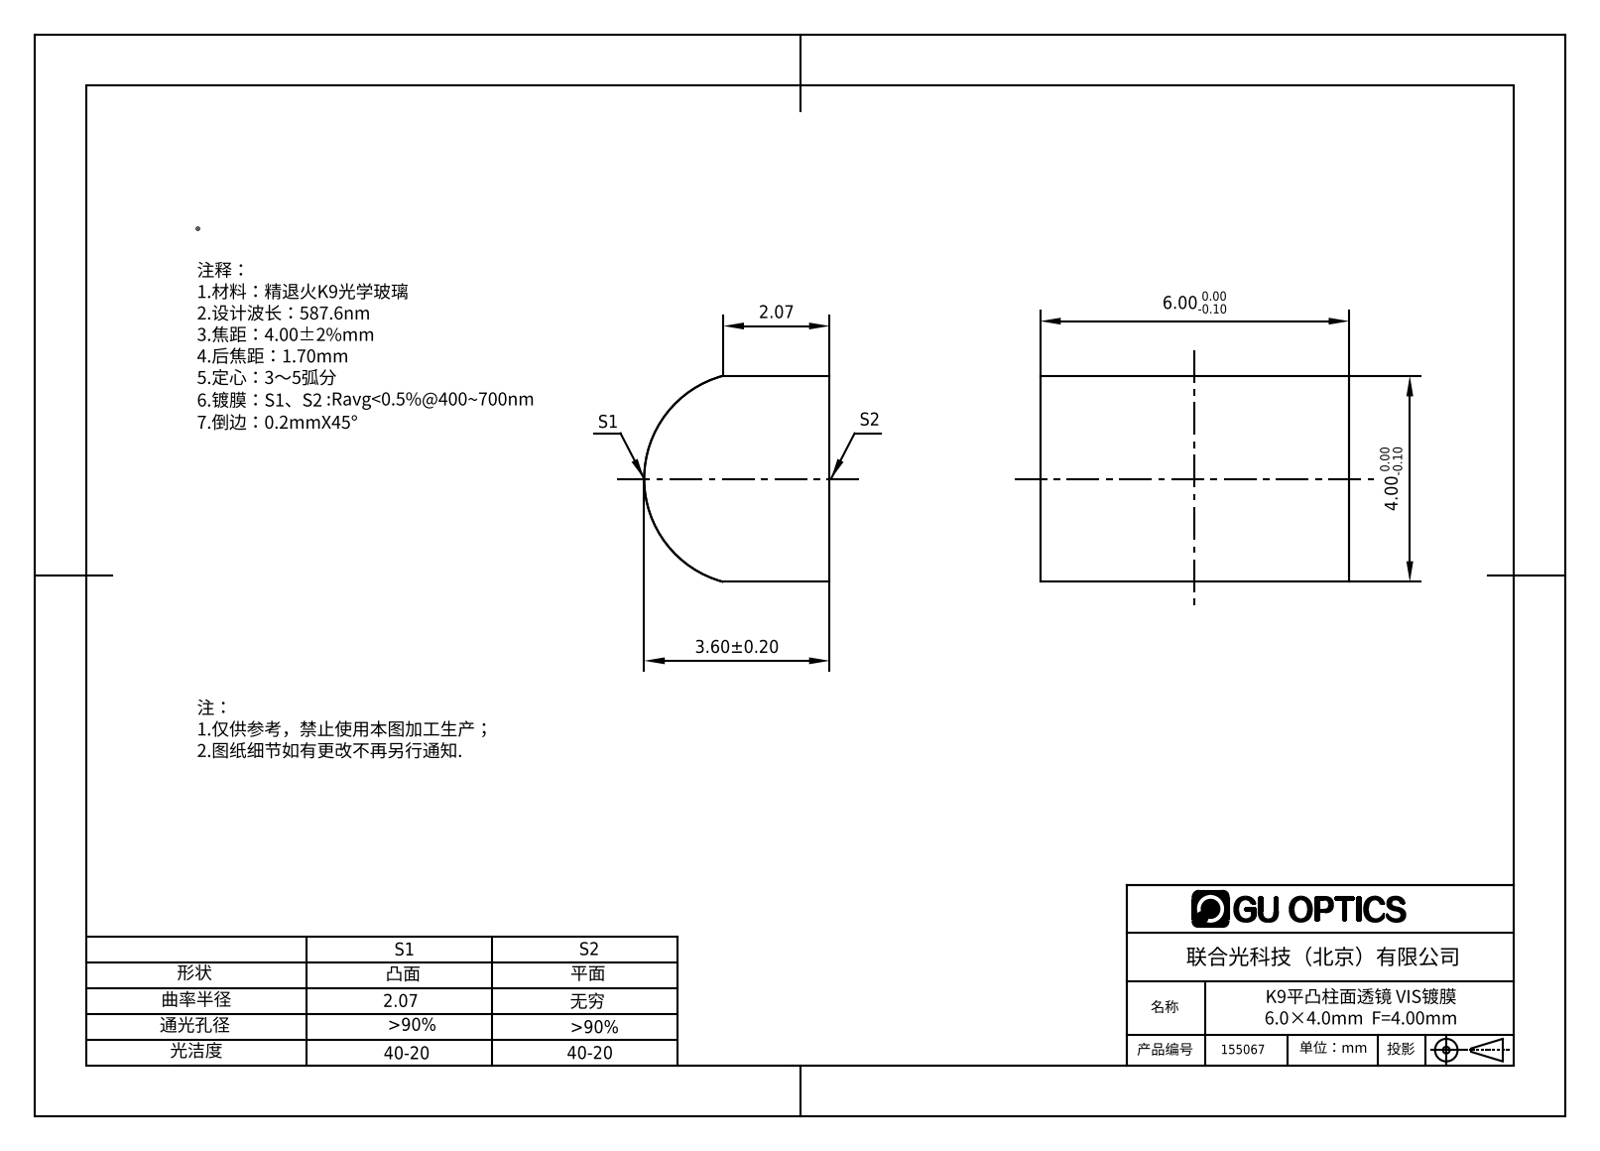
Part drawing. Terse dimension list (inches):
name: 155001
written by: SolidWorks 2016 (AUTOMOTIVE_DESIGN)
unit: in
bodies: 1 solid, 6 faces (5 planar, 1 cylindrical, 0 other)
size: 0.236 × 0.157 × 0.142
volume: 0.005 in³; area: 0.166 in²
rounds: 1× R0.081
face distances: 0.236, 0.157
